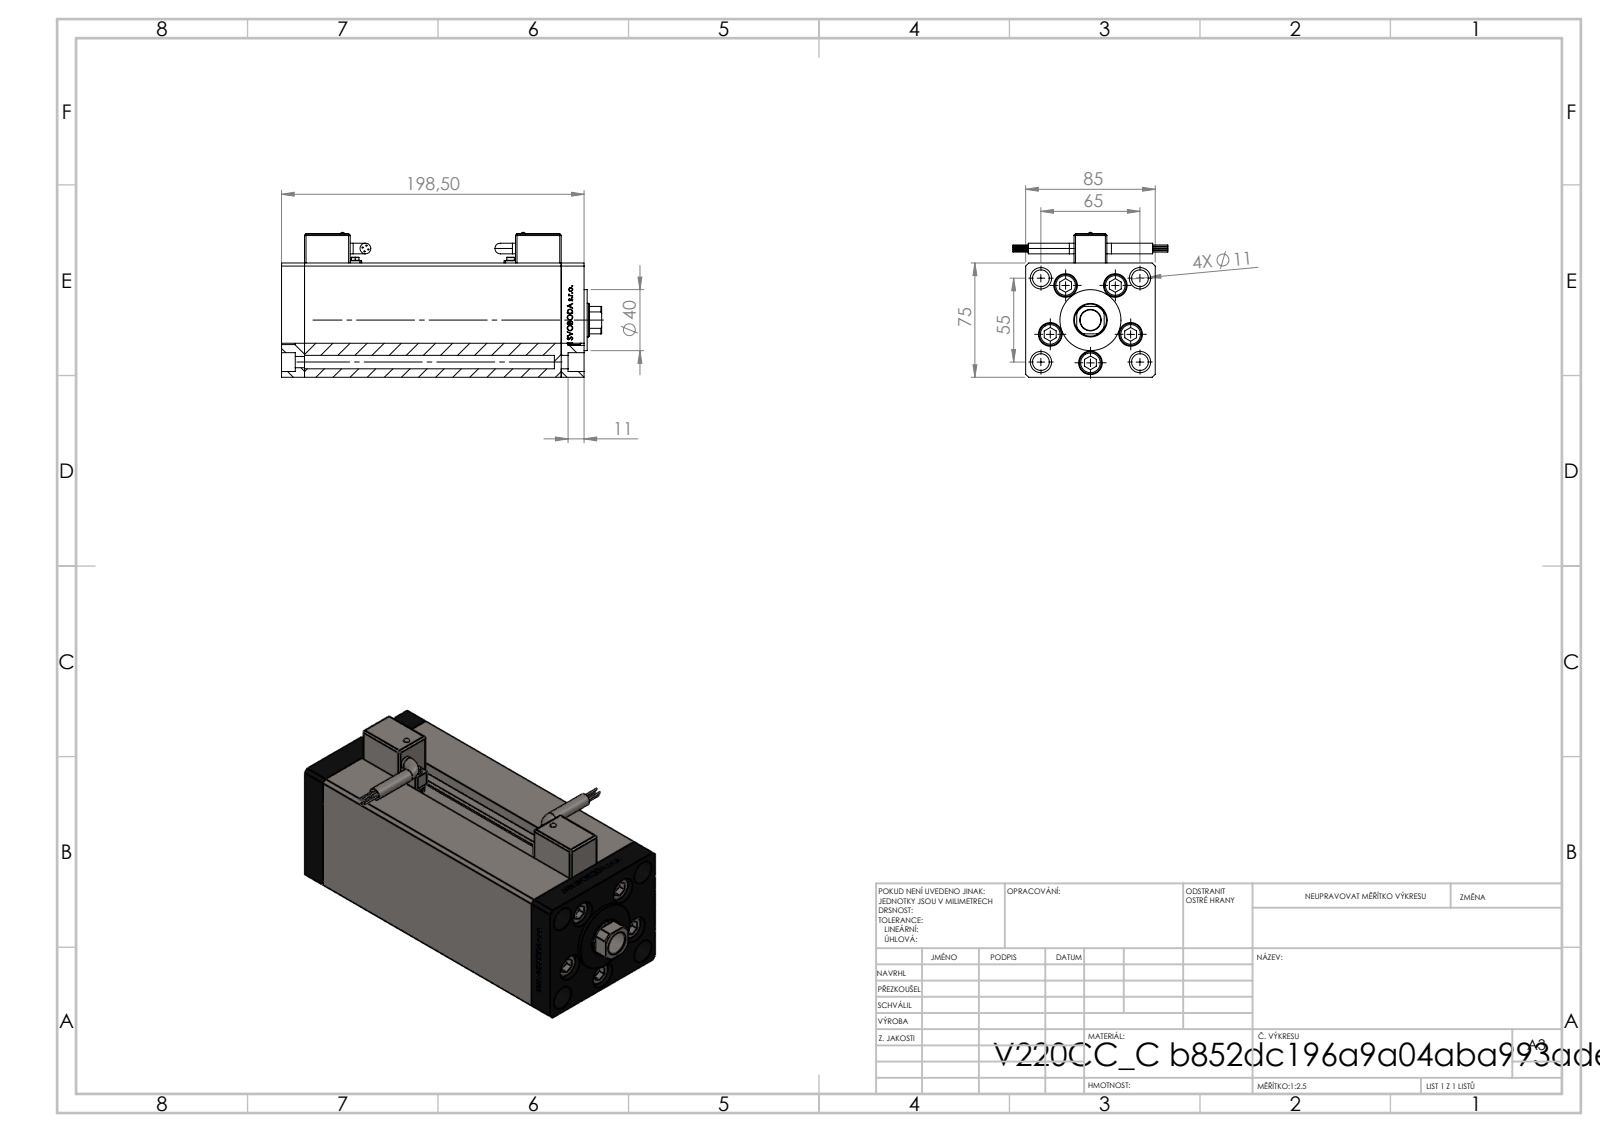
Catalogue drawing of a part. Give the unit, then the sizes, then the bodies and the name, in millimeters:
Units: millimetres
Overall size (bounding box): 210 × 101.6 × 95.1
Round holes (diameter × count): ⌀11 ×9, ⌀15.5 ×5, ⌀10 ×4, ⌀14 ×4, ⌀3.6 ×2, ⌀5 ×2, ⌀7 ×2, ⌀13.5 ×1, ⌀14.5 ×1, ⌀22 ×1
Round bosses / shafts (diameter × count): ⌀0.85 ×8, ⌀8 ×5, ⌀14.5 ×4, ⌀7 ×4, ⌀6 ×2, ⌀3.5 ×2, ⌀2.5 ×2, ⌀40 ×1
Partial cylindrical surfaces — rounded edges, fillets, slot ends (radius × count): R1 ×24, R4 ×4, R0.93 ×2, R10.5 ×1
Main face-to-face distances: 85, 75, 168.5, 15, 183.5, 10.5, 68.5, 198.5, 34.25, 6.5
Hole centre spacings: 28, 42.57, 8.25, 16.86, 19.17, 32.33, 32.5, 33.63
Volume: 1 087 000 mm³ · Surface area: 204 172 mm²
Bodies: 15 solids, 1367 faces (620 planar, 249 cylindrical, 498 other)
Part name (STEP PRODUCT): V220C_C MIDDLE; Magnetic_Switch_MSU4; ALLEN BOLT; V220C FRONT (+2 more)
STEP written by: SolidWorks 2019 (CONFIG_CONTROL_DESIGN)
